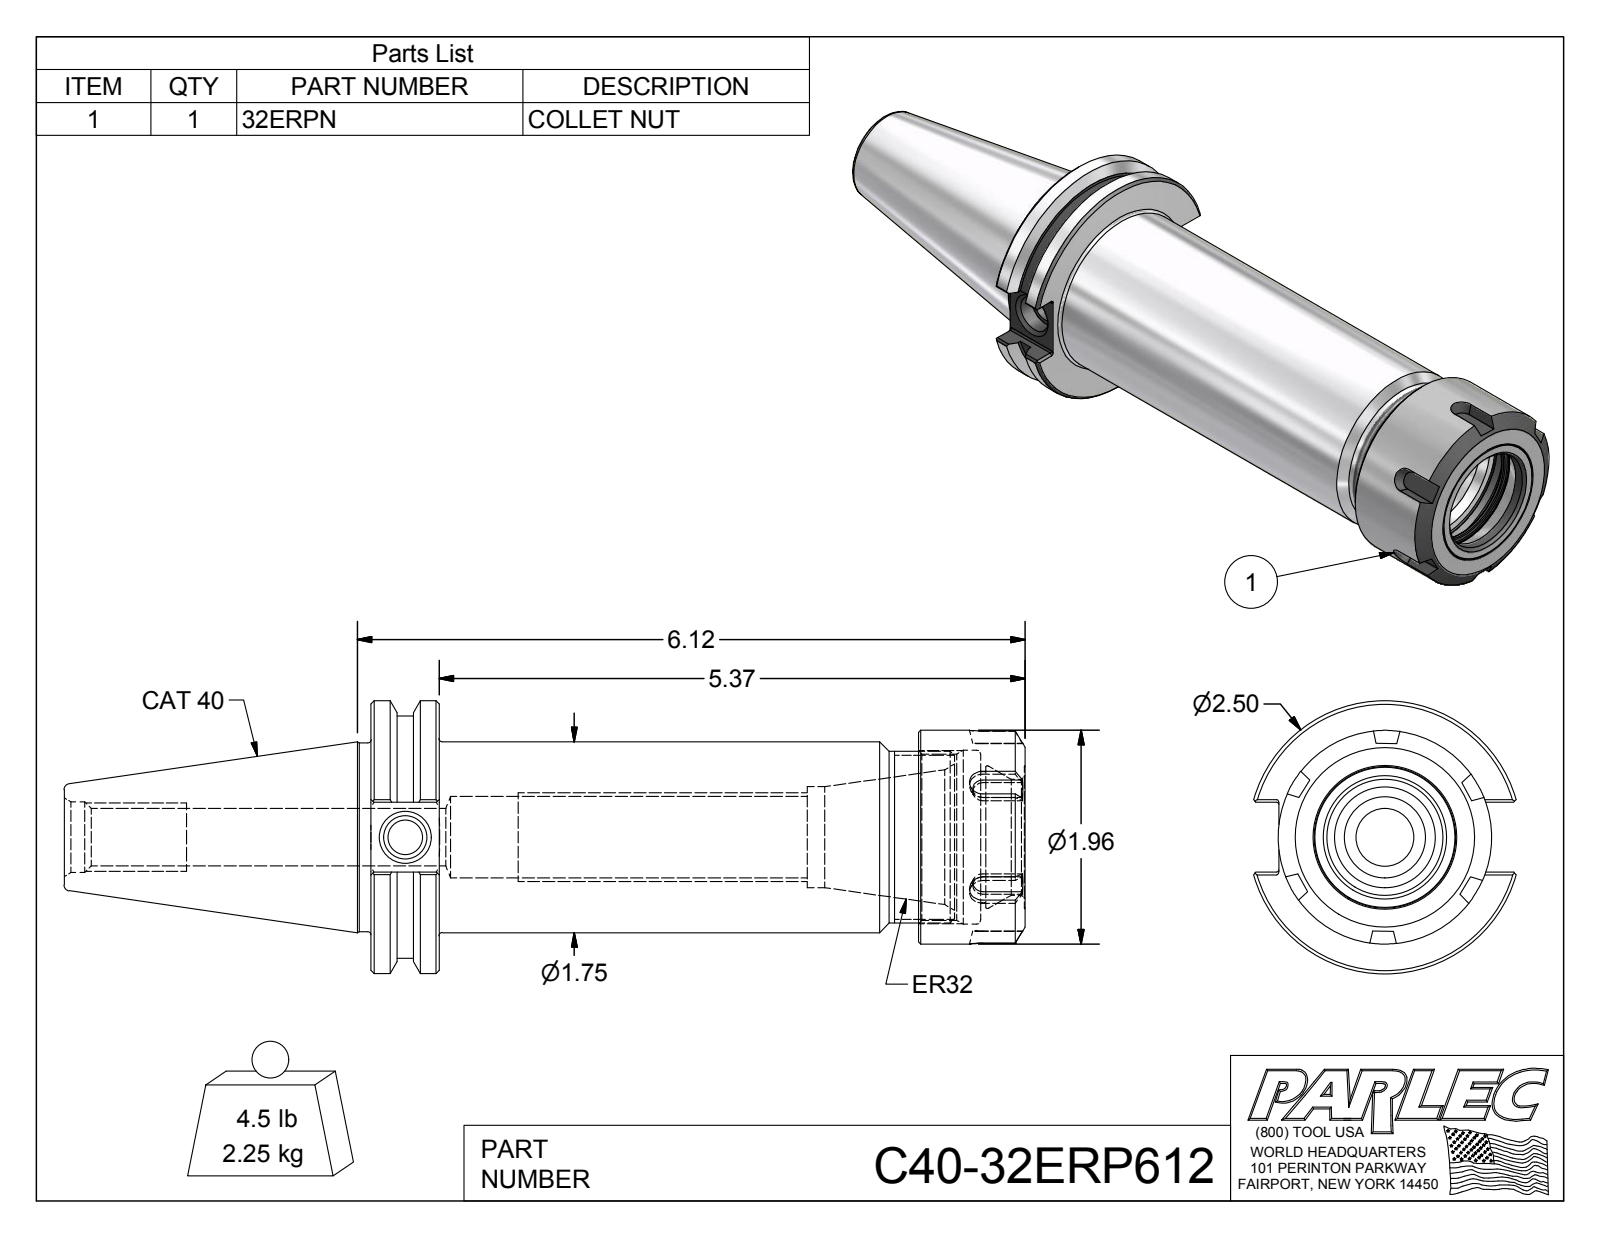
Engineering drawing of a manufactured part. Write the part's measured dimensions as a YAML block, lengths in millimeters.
part_name: "C40-32ERP612; C40-32ER6-1; 32ERPN"
step_written_by: "Autodesk Inventor 2012 (AUTOMOTIVE_DESIGN)"
units: millimeters
bodies: {solids: 2, faces: 129, planar: 55, cylindrical: 33, other: 41}
overall_size: [223.7, 63.5, 61]
volume: 259400
surface_area: 53330
round_holes:
  - {diameter: 8, count: 1}
  - {diameter: 10.1, count: 1}
  - {diameter: 13.4, count: 1}
  - {diameter: 16.5, count: 1}
  - {diameter: 18.9, count: 1}
  - {diameter: 23.5, count: 1}
  - {diameter: 27, count: 1}
  - {diameter: 30.5, count: 1}
  - {diameter: 33.1, count: 1}
  - {diameter: 38.7, count: 1}
  - {diameter: 40.5, count: 1}
round_bosses_or_shafts:
  - {diameter: 63.5, count: 1}
  - {diameter: 56.4, count: 1}
  - {diameter: 49.7, count: 1}
  - {diameter: 44.5, count: 1}
  - {diameter: 43.9, count: 1}
  - {diameter: 40, count: 1}
partial_cylinders:
  - {radius: 0.5, count: 12}
face_to_face_distances: [15.9, 152.3, 136.4, 127.4, 111.6, 24.8, 141.9, 126.1, 14.5, 10.3]
